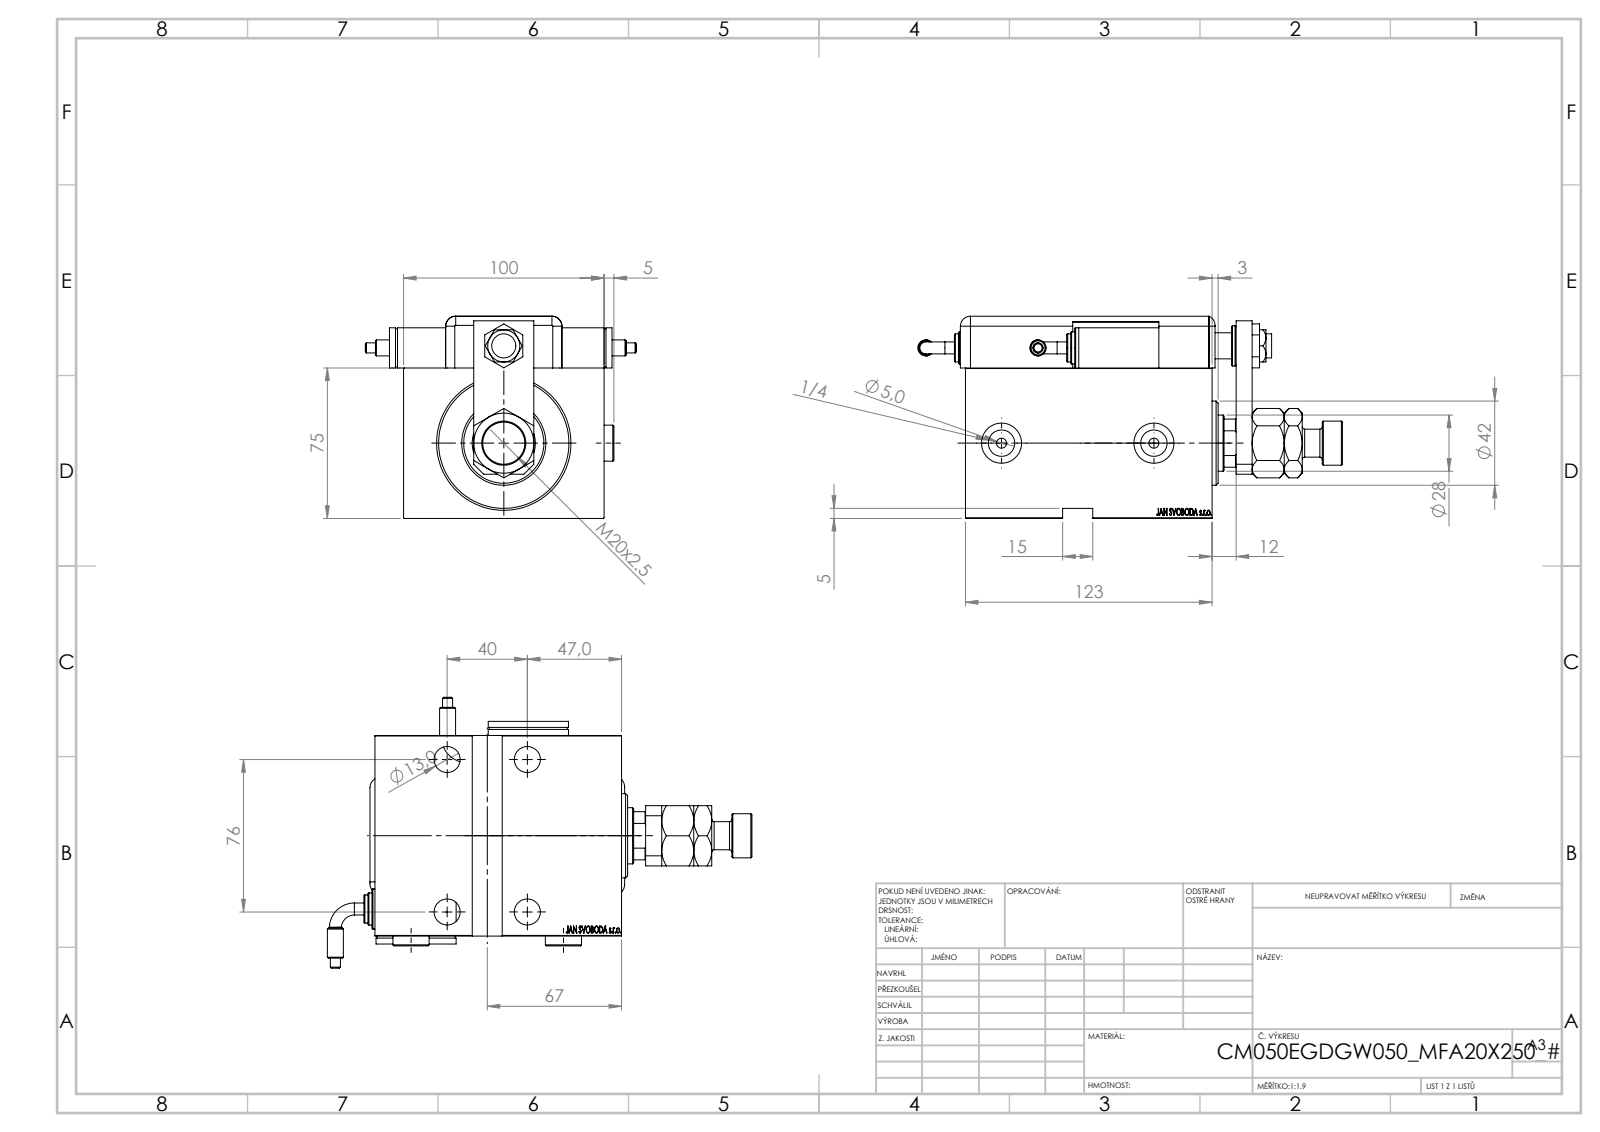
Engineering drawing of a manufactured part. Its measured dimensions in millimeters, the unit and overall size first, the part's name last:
Units: millimetres
Overall size (bounding box): 211.76 × 135.01 × 100.8
Round holes (diameter × count): ⌀13 ×5, ⌀19 ×4, ⌀20 ×3, ⌀4 ×2, ⌀5 ×2, ⌀8 ×2, ⌀13.16 ×2, ⌀12 ×1, ⌀14 ×1, ⌀18.5 ×1, ⌀28 ×1, ⌀31.5 ×1
Round bosses / shafts (diameter × count): ⌀20 ×3, ⌀14 ×3, ⌀18 ×2, ⌀16 ×2, ⌀8 ×2, ⌀6 ×2, ⌀5.04 ×2, ⌀52 ×1
Partial cylindrical surfaces — rounded edges, fillets, slot ends (radius × count): R5 ×9, R10 ×1, R13.5 ×1
Main face-to-face distances: 3, 75, 100, 14, 20, 123, 100.8, 25.8, 109, 25
Hole centre spacings: 76, 40, 47.2, 61.22, 82.87, 85.88, 91.59, 20
Volume: 977 955 mm³ · Surface area: 190 056 mm²
Bodies: 16 solids, 1376 faces (672 planar, 135 cylindrical, 569 other)
Part name (STEP PRODUCT): Zatka_OIL_PORT; NUT_D13; Q_T_W_MFA; ZARAZKA_Q (+7 more)
STEP written by: SolidWorks 2019 (CONFIG_CONTROL_DESIGN)
